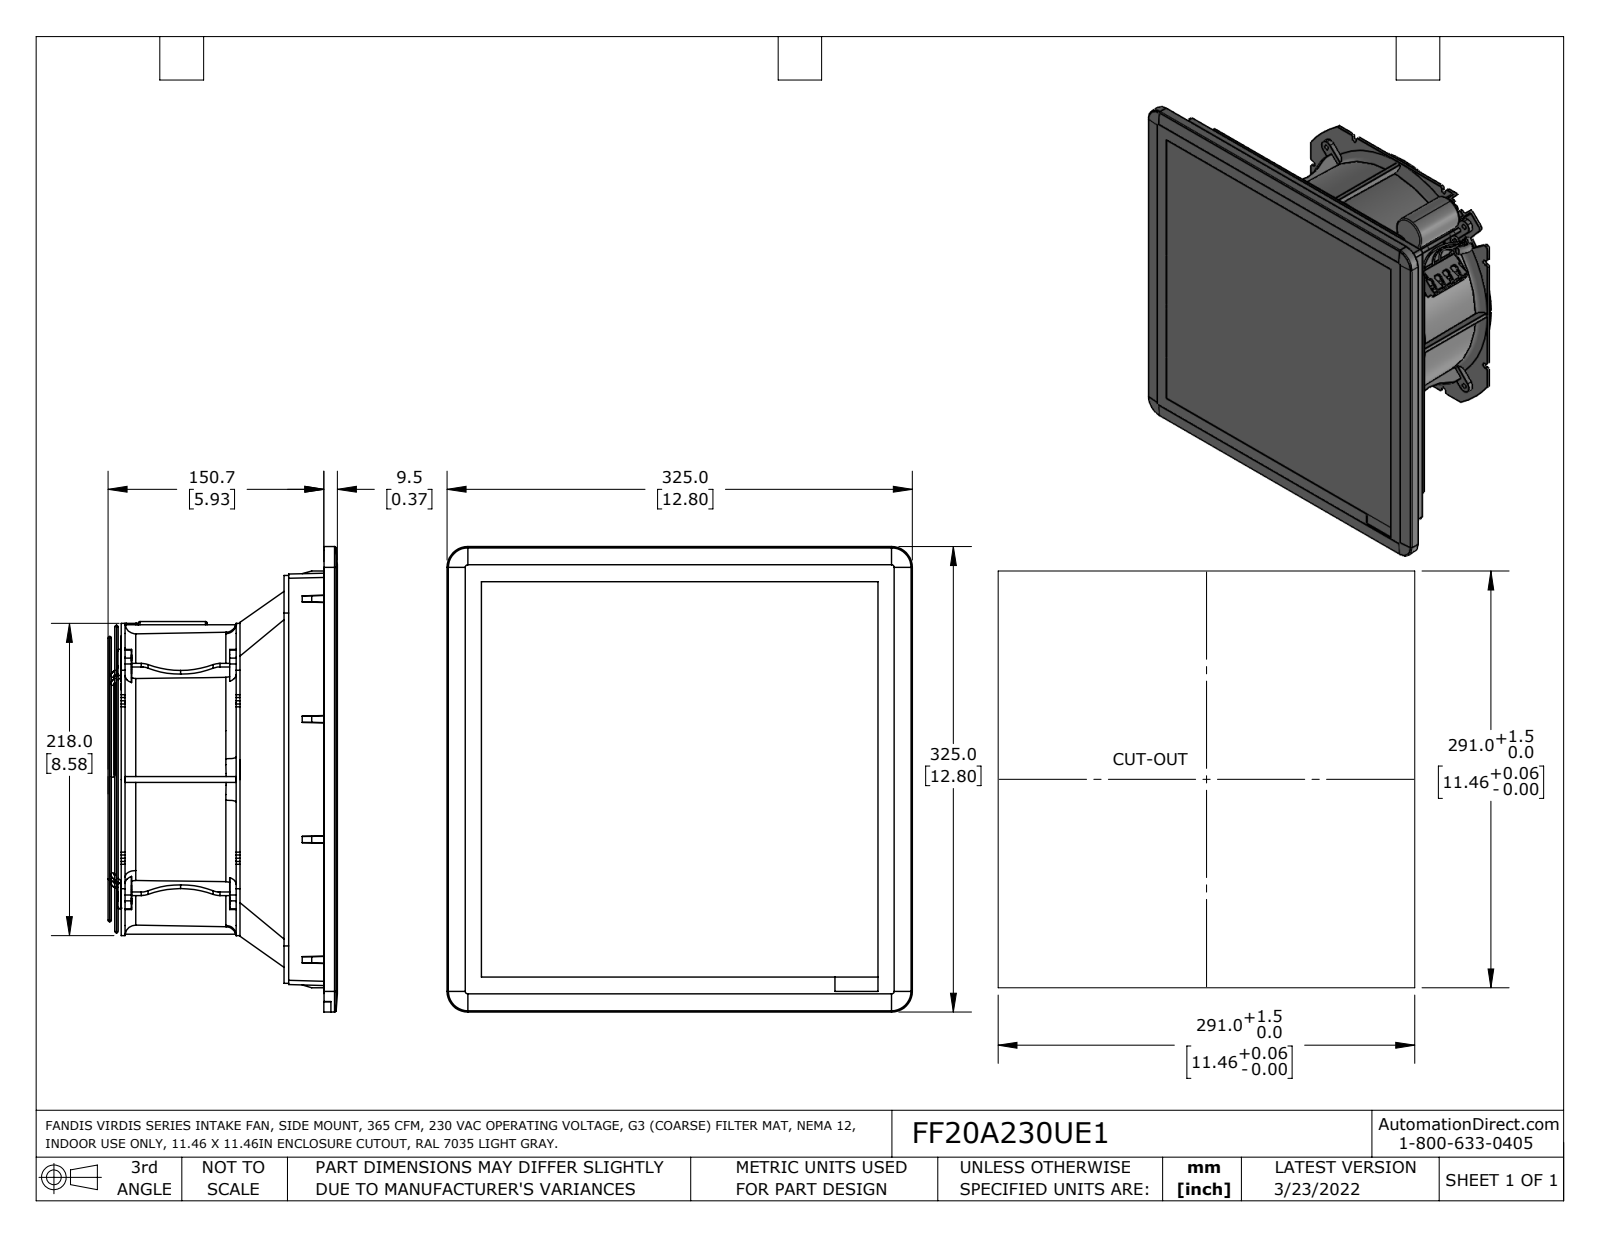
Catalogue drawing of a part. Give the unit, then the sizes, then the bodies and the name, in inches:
Units: inches
Overall size (bounding box): 12.795 × 12.795 × 6.306
Round holes (diameter × count): ⌀0.177 ×4, ⌀0.142 ×2
Round bosses / shafts (diameter × count): ⌀1.181 ×1, ⌀0.315 ×1
Partial cylindrical surfaces — rounded edges, fillets, slot ends (radius × count): R0.079 ×16, R0.039 ×14, R0.047 ×12, R0.016 ×9, R0.059 ×8, R0.089 ×8, R0.394 ×8, R0.738 ×8
Main face-to-face distances: 5.933, 0.362, 5.571, 0.374, 5.945, 1.469, 1.457, 1.094, 4.476, 4.37
Hole centre spacings: 6.681, 9.448, 2.319
Volume: 482.5 in³ · Surface area: 650.7 in²
Bodies: 6 solids, 879 faces (358 planar, 252 cylindrical, 269 other)
Part name (STEP PRODUCT): FF20AxxxyE
STEP written by: SolidWorks 2021 (AUTOMOTIVE_DESIGN)
